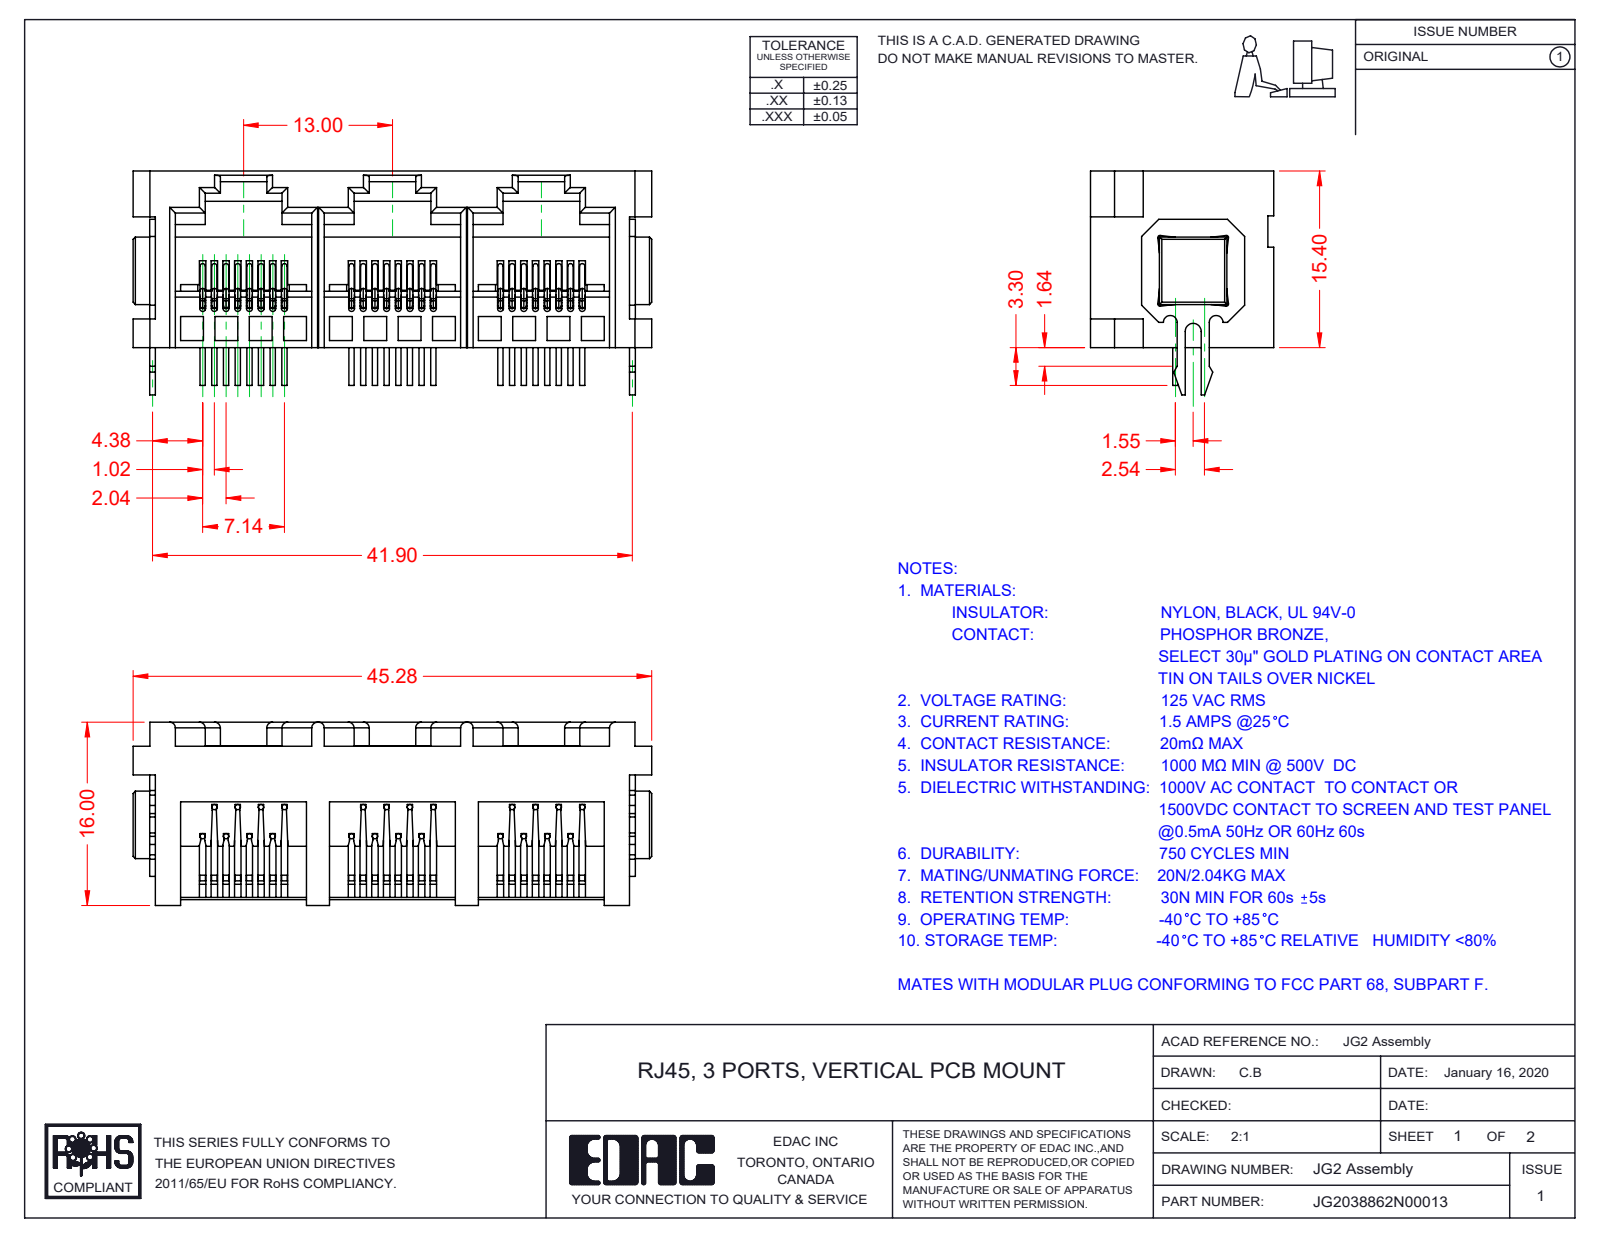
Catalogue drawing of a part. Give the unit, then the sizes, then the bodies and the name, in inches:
Units: inches
Overall size (bounding box): 1.783 × 0.769 × 0.63
Round bosses / shafts (diameter × count): ⌀0.018 ×96
Partial cylindrical surfaces — rounded edges, fillets, slot ends (radius × count): R0.02 ×69, R0.008 ×4, R0.801 ×4, R0.012 ×3, R0.024 ×2, R0.008 ×1, R0.018 ×1, R0.028 ×1
Main face-to-face distances: 0.512, 0.472, 0.02, 0.134, 0.087, 0.436, 0.036, 1.024, 0.433, 0.079
Volume: 0.298 in³ · Surface area: 14.84 in²
Bodies: 30 solids, 1835 faces (1210 planar, 457 cylindrical, 168 other)
Part name (STEP PRODUCT): G2 Contact Lock; G2 Contacts; G2 Boardlock2; G2 Boardlock1 (+2 more)
STEP written by: SolidWorks 2016 (CONFIG_CONTROL_DESIGN)
